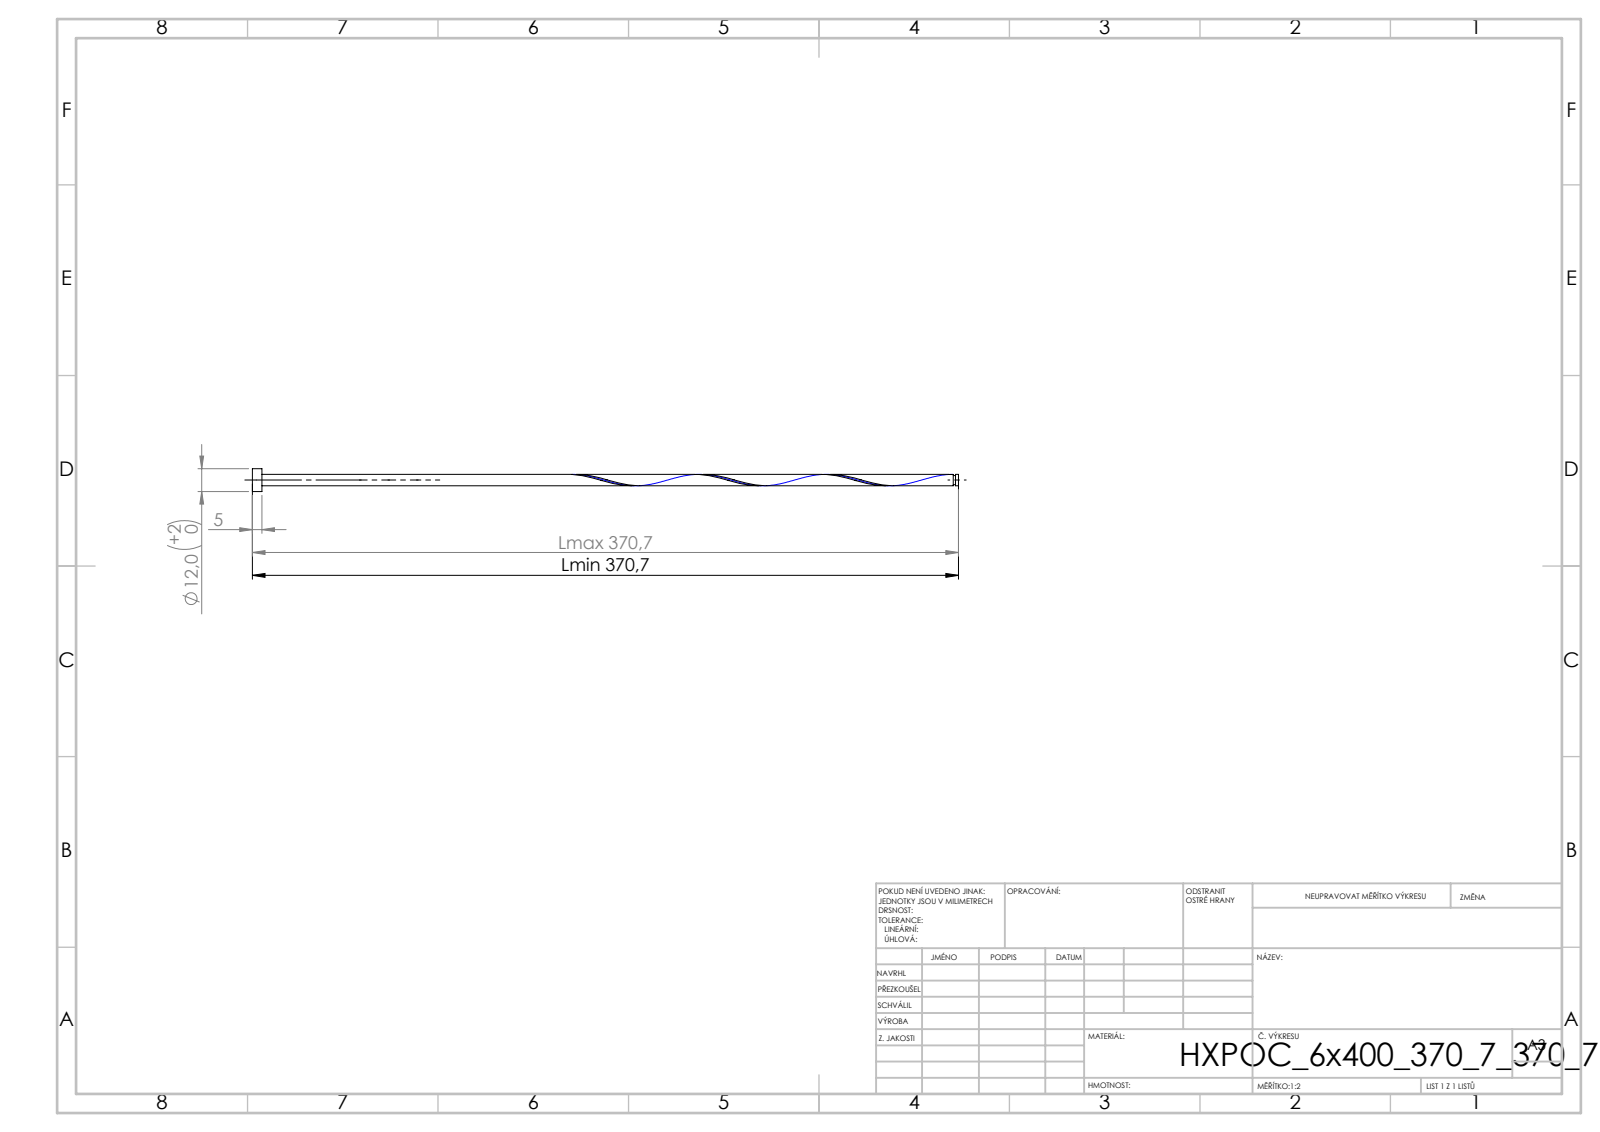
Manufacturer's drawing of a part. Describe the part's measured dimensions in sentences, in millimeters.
Its 3-D file was written by "SolidWorks 2019 (CONFIG_CONTROL_DESIGN)". It is 1 solid with 16 faces: 6 planar, 9 cylindrical and 1 other. Overall it measures 370.7 by 12 by 12 millimeters. Its volume is 13 299 cubic millimeters and its surface area 9 957 square millimeters. Round bosses or shafts: 1 of diameter 12, 1 of diameter 6, 1 of diameter 4.8. The main face-to-face distances are 5, 370.7, 365.7, 369.12, 364.12, 1.58, 367.92, 362.92, 1.2, 2.78.
